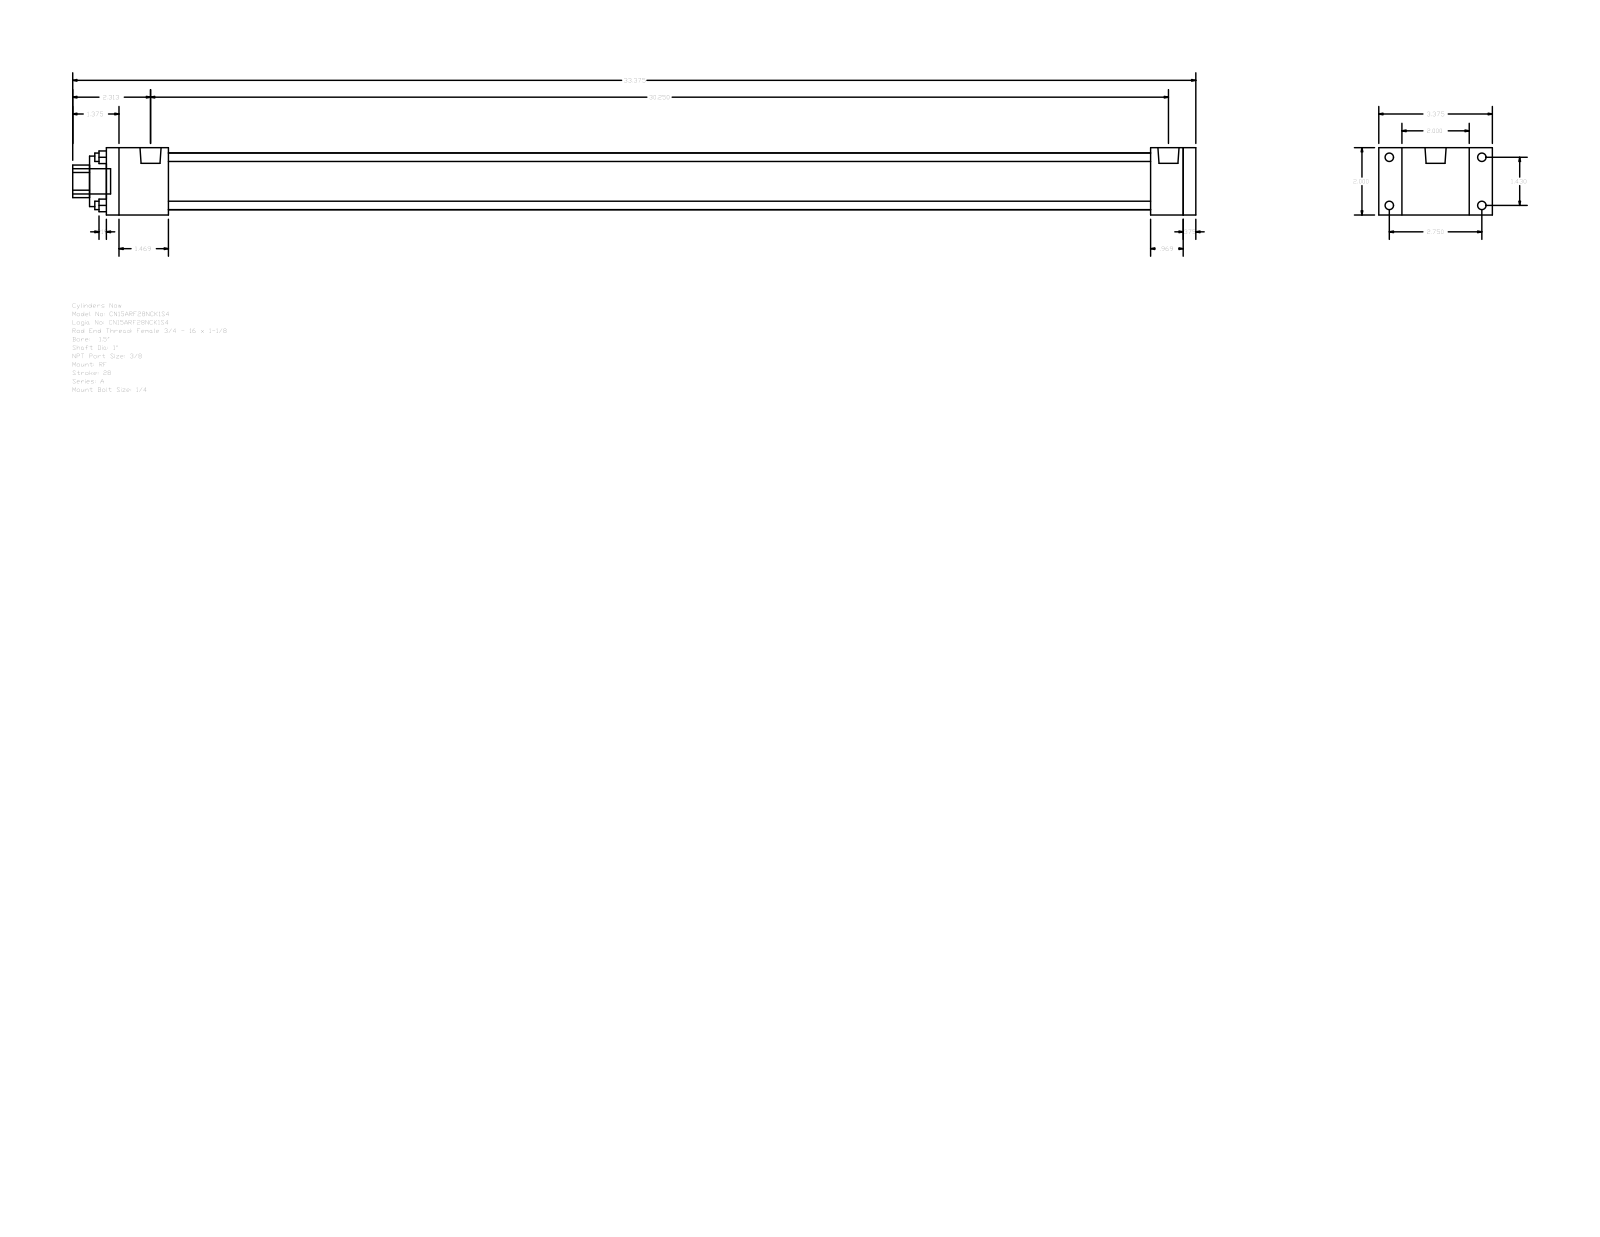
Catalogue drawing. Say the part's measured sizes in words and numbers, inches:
The part is named "A_RF__0150_1". Its 3-D file was written by "GSSL Pune (CONFIG_CONTROL_DESIGN)". It is 0 solids with 92 faces: 64 planar, 28 cylindrical and 0 other. Overall it measures 33.375 by 3.375 by 2 inches. Round holes: 4 of diameter 0.25, 1 of diameter 1, 1 of diameter 1.5, 1 of diameter 1.69. Round bosses or shafts: 4 of diameter 0.25, 4 of diameter 0.219, 2 of diameter 0.627, 1 of diameter 0.75. Partial cylindrical surfaces (rounded edges, fillets, slot ends): 1 of radius 0.484. The main face-to-face distances are 2, 0.375, 32, 32.375, 31.031, 0.969, 1.344, 1.844, 29.187, 30.156. The hole center spacings are 1.011, 1.43, 2.022.
